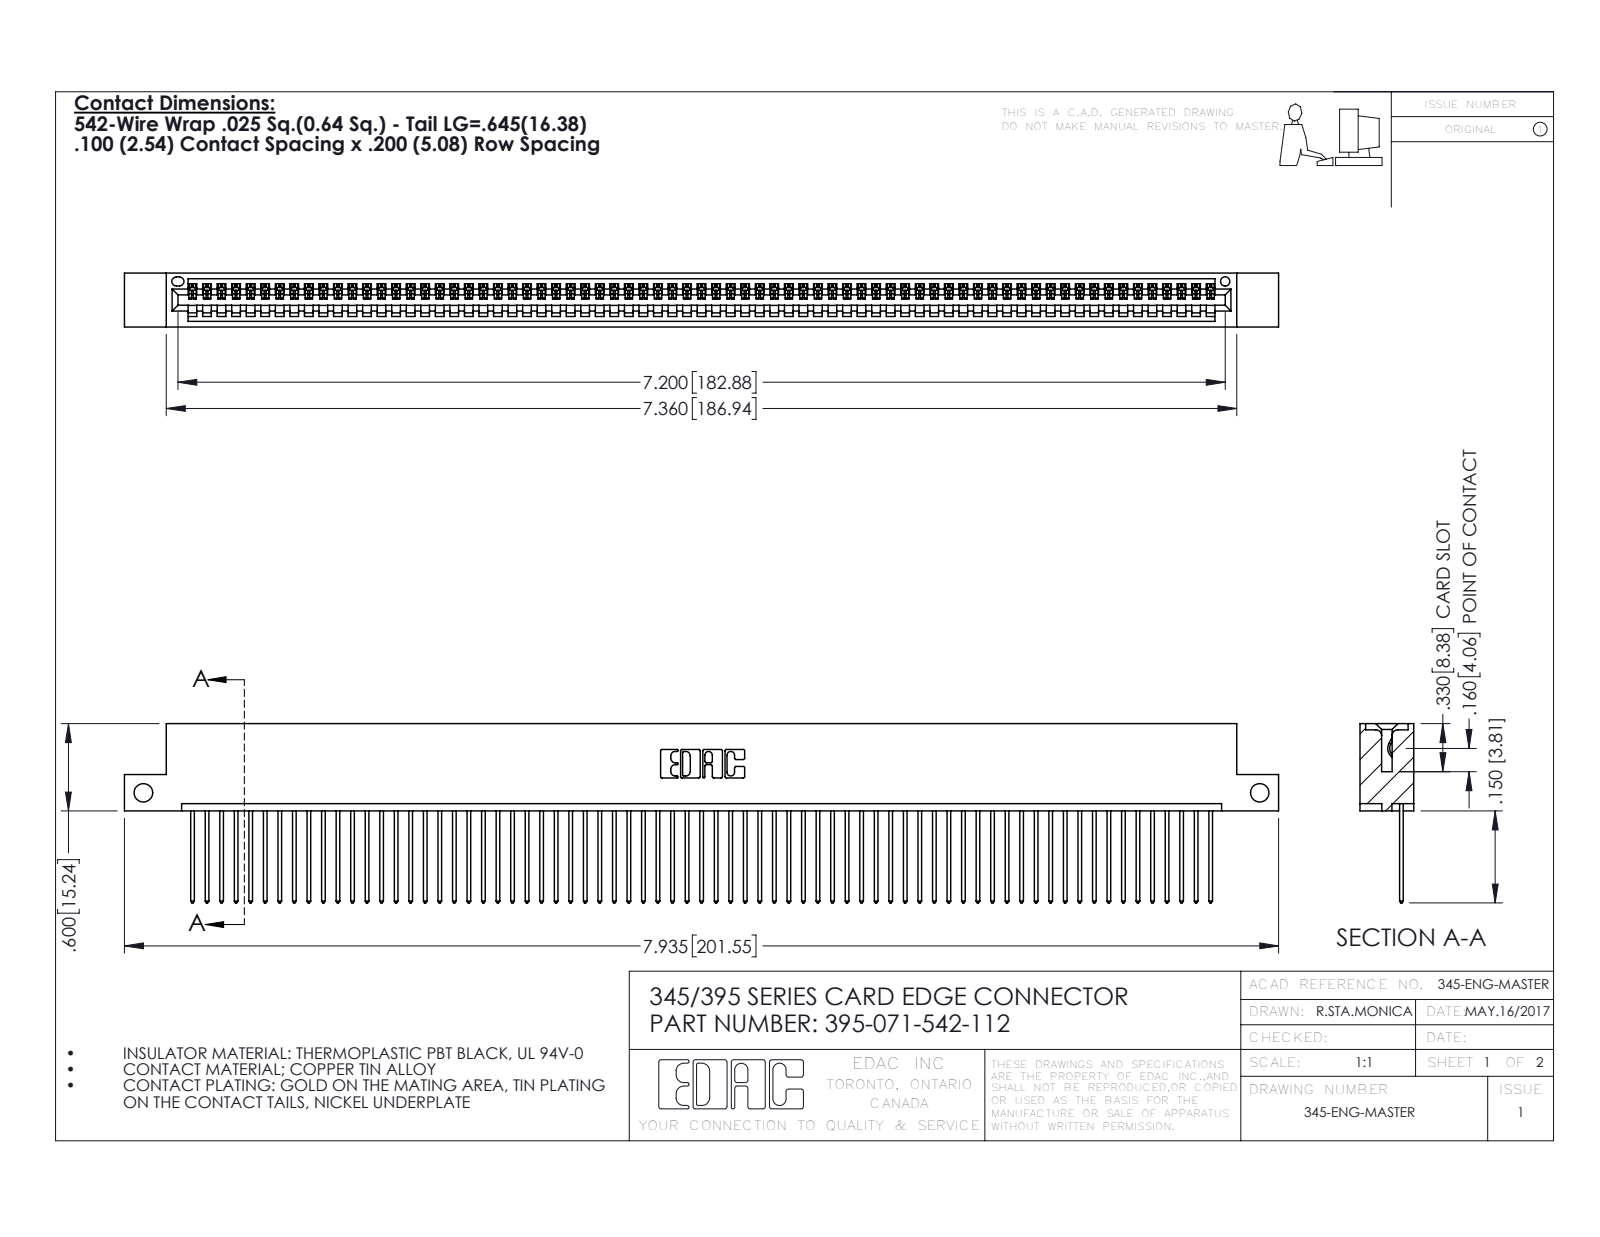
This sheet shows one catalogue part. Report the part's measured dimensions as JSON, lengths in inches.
{"part_name": "395-071-542-112; 345 Part_Flush Mounting Lugs - Side Mount; 345-292-001_345-293-142", "step_written_by": "SolidWorks 2016 (CONFIG_CONTROL_DESIGN)", "units": "inches", "bodies": {"solids": 72, "faces": 4244, "planar": 2920, "cylindrical": 1324, "other": 0}, "overall_size": [7.935, 1.232, 0.37], "volume_in3": 1.187, "surface_area_in2": 42.01, "round_holes": [[0.128, 2], [0.064, 1]], "partial_cylinders_radius": [[0.006, 142], [0.01, 142], [0.01, 22], [0.007, 6], [0.031, 6], [0.026, 3], [0.031, 2], [0.04, 2]], "face_to_face_distances": [0.072, 0.298, 0.098, 0.272, 0.025, 0.37, 0.2, 0.225, 0.149, 0.072], "hole_center_spacings": [7.675]}
